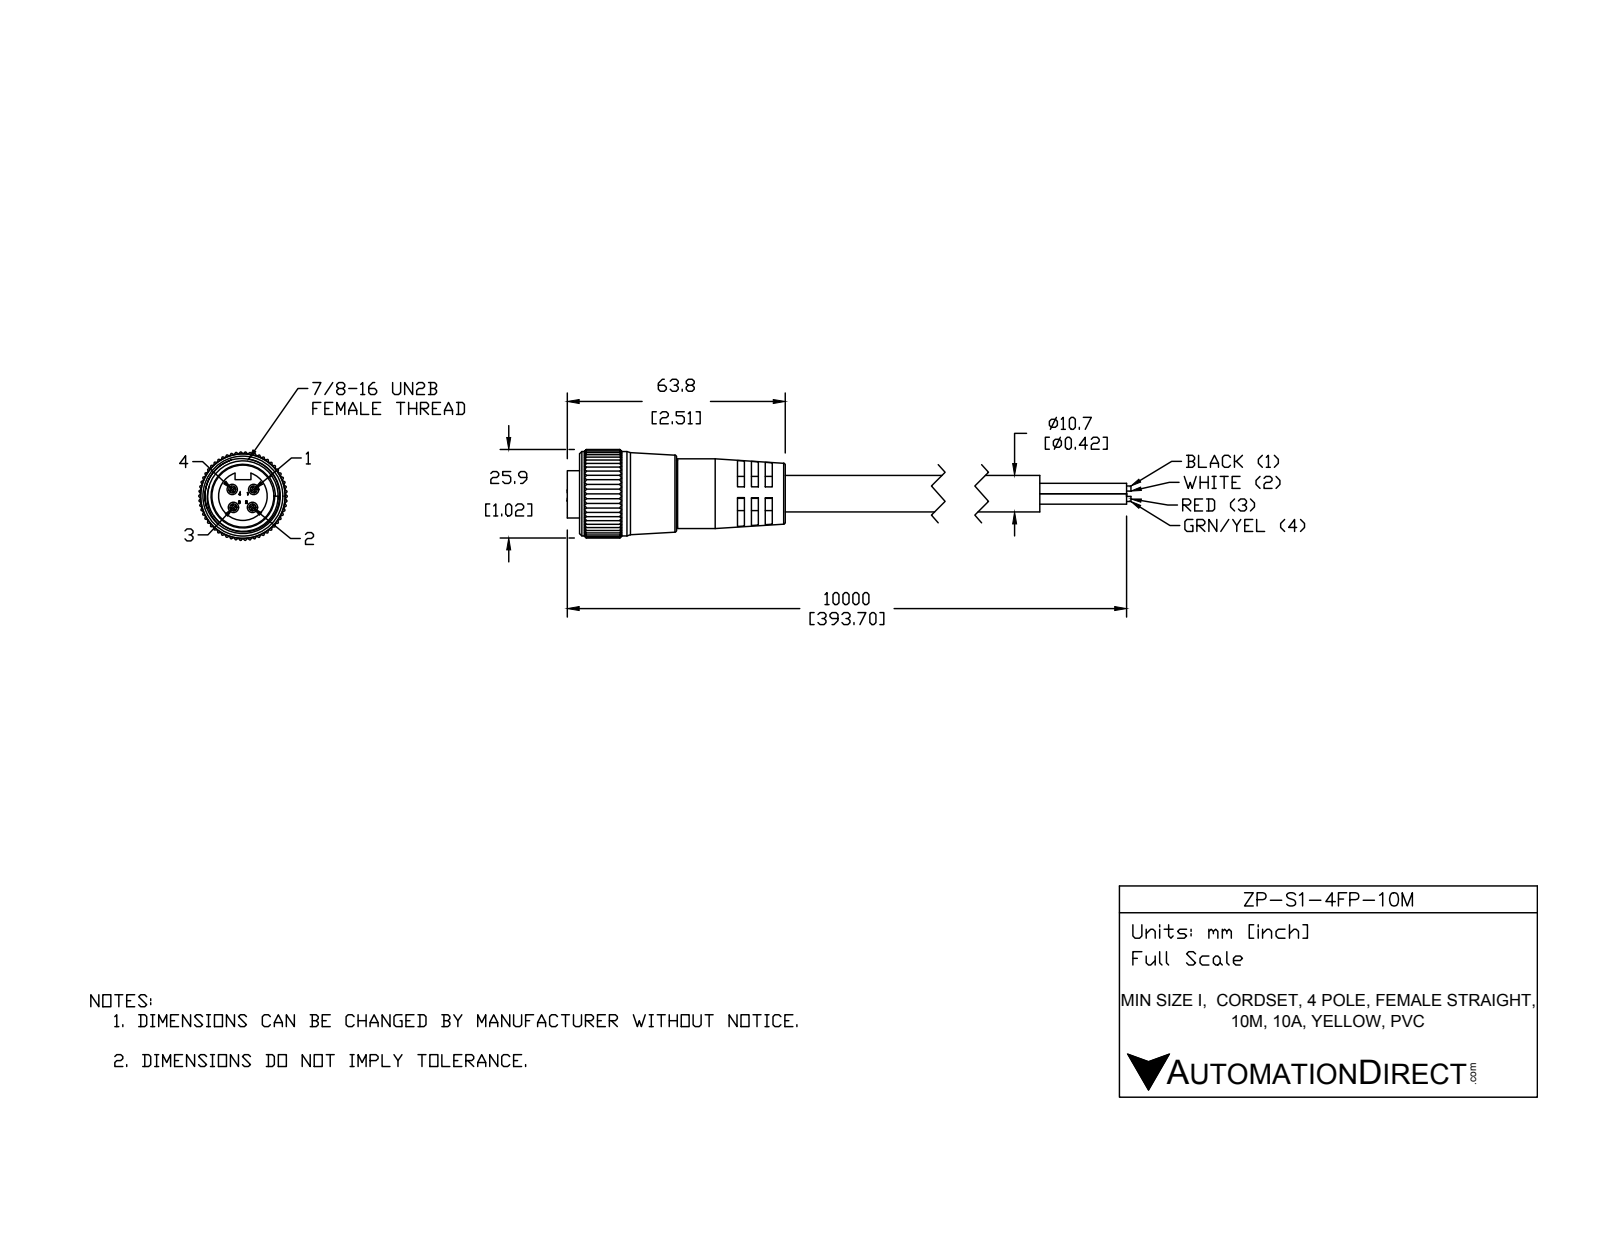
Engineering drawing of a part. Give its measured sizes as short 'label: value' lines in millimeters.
name: ZP-S1-4FP-10M
written by: SolidWorks 2015 (AUTOMOTIVE_DESIGN)
unit: mm
bodies: 2 solids, 558 faces (208 planar, 308 cylindrical, 42 other)
size: 109.09 × 52.91 × 25.84
volume: 27 613 mm³; area: 12 011 mm²
holes: 4× ⌀3.05, 1× ⌀18.14, 1× ⌀20.58, 1× ⌀21
bosses: 2× ⌀10.67, 1× ⌀24.68, 1× ⌀20.4, 1× ⌀19.5, 1× ⌀14.22
rounds: 165× R0.25, 1× R5.25, 1× R12.93
face distances: 4.03, 2, 2.03, 6.03, 8.06, 13.87, 11.87, 9.84, 7.84, 6.06
hole spacings: 3.67, 5.24, 4.32, 4.33, 5.59, 6.24, 7.89, 7.9
